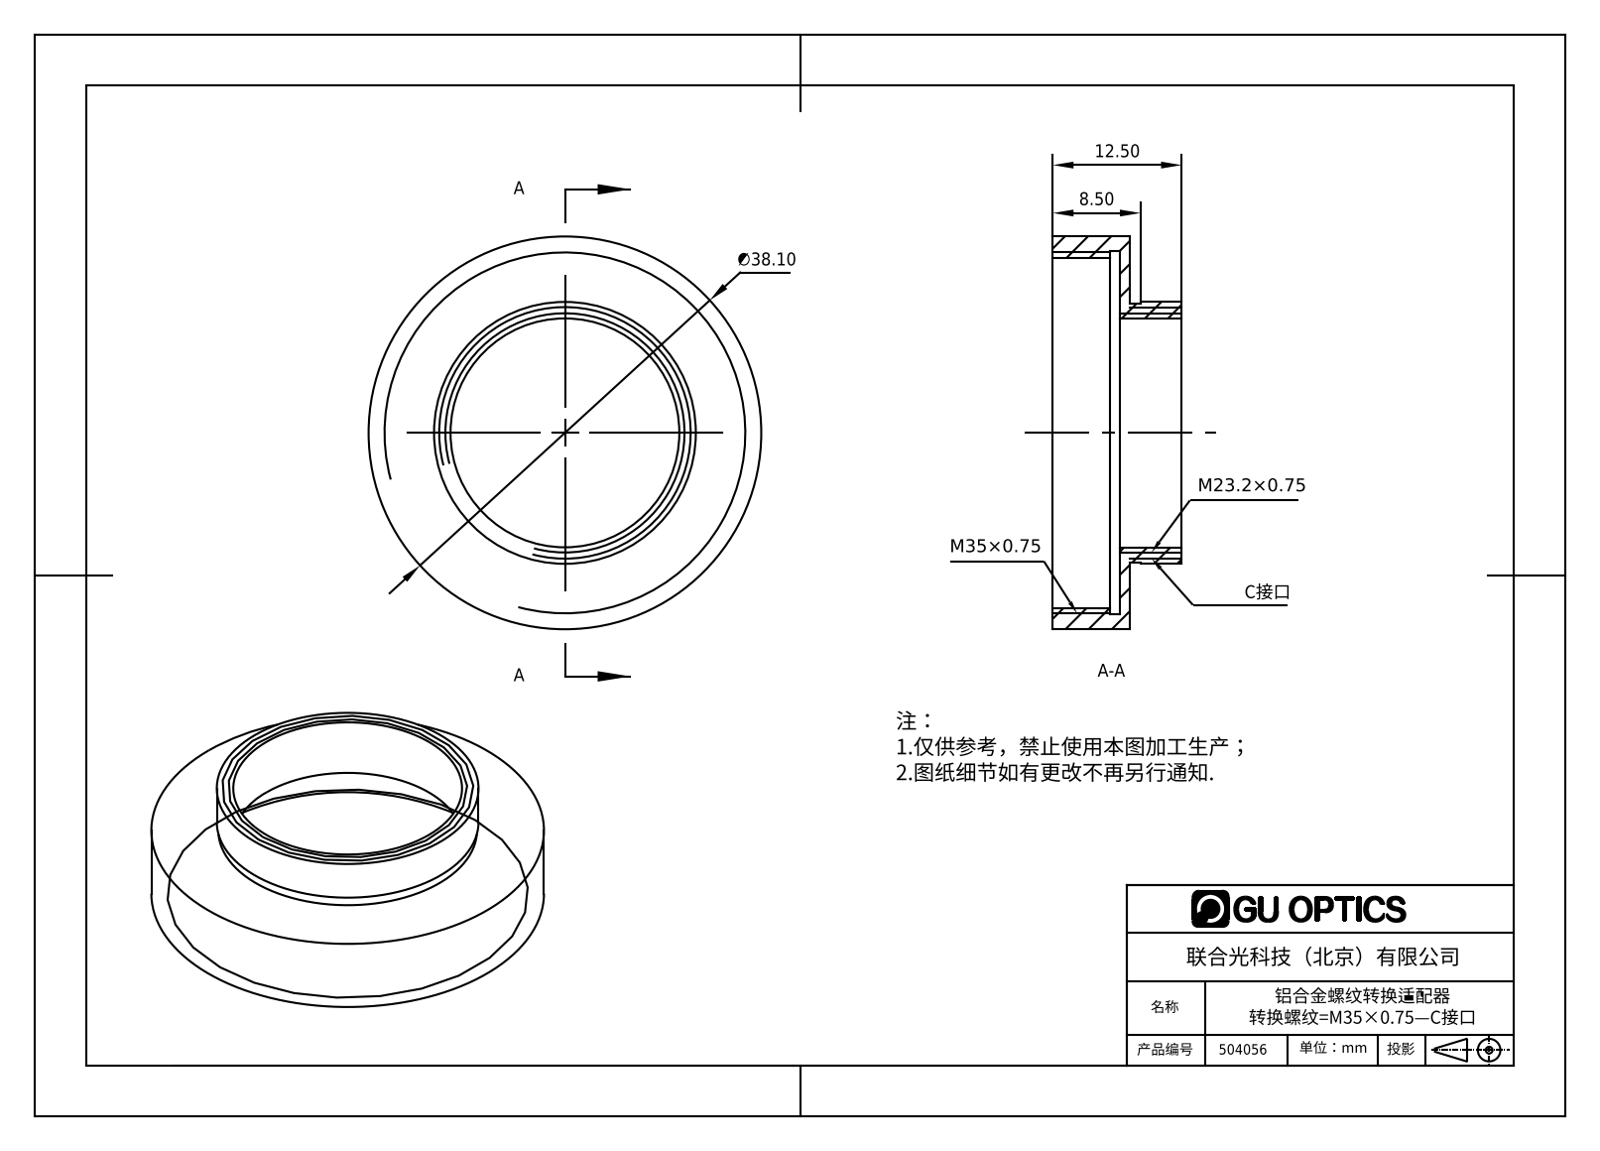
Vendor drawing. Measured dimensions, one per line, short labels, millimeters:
name: 504056
written by: SolidWorks 2016 (AUTOMOTIVE_DESIGN)
unit: mm
bodies: 1 solid, 18 faces (6 planar, 12 cylindrical, 0 other)
size: 38.1 × 38.1 × 12.5
volume: 2 783 mm³; area: 4 073 mm²
holes: 1× ⌀22.2, 1× ⌀34, 1× ⌀35.2
bosses: 1× ⌀38.1, 1× ⌀25.4, 1× ⌀25.1
face distances: 1, 6.5, 7.5, 12.5, 6, 5, 2, 5.5, 7, 8.5
